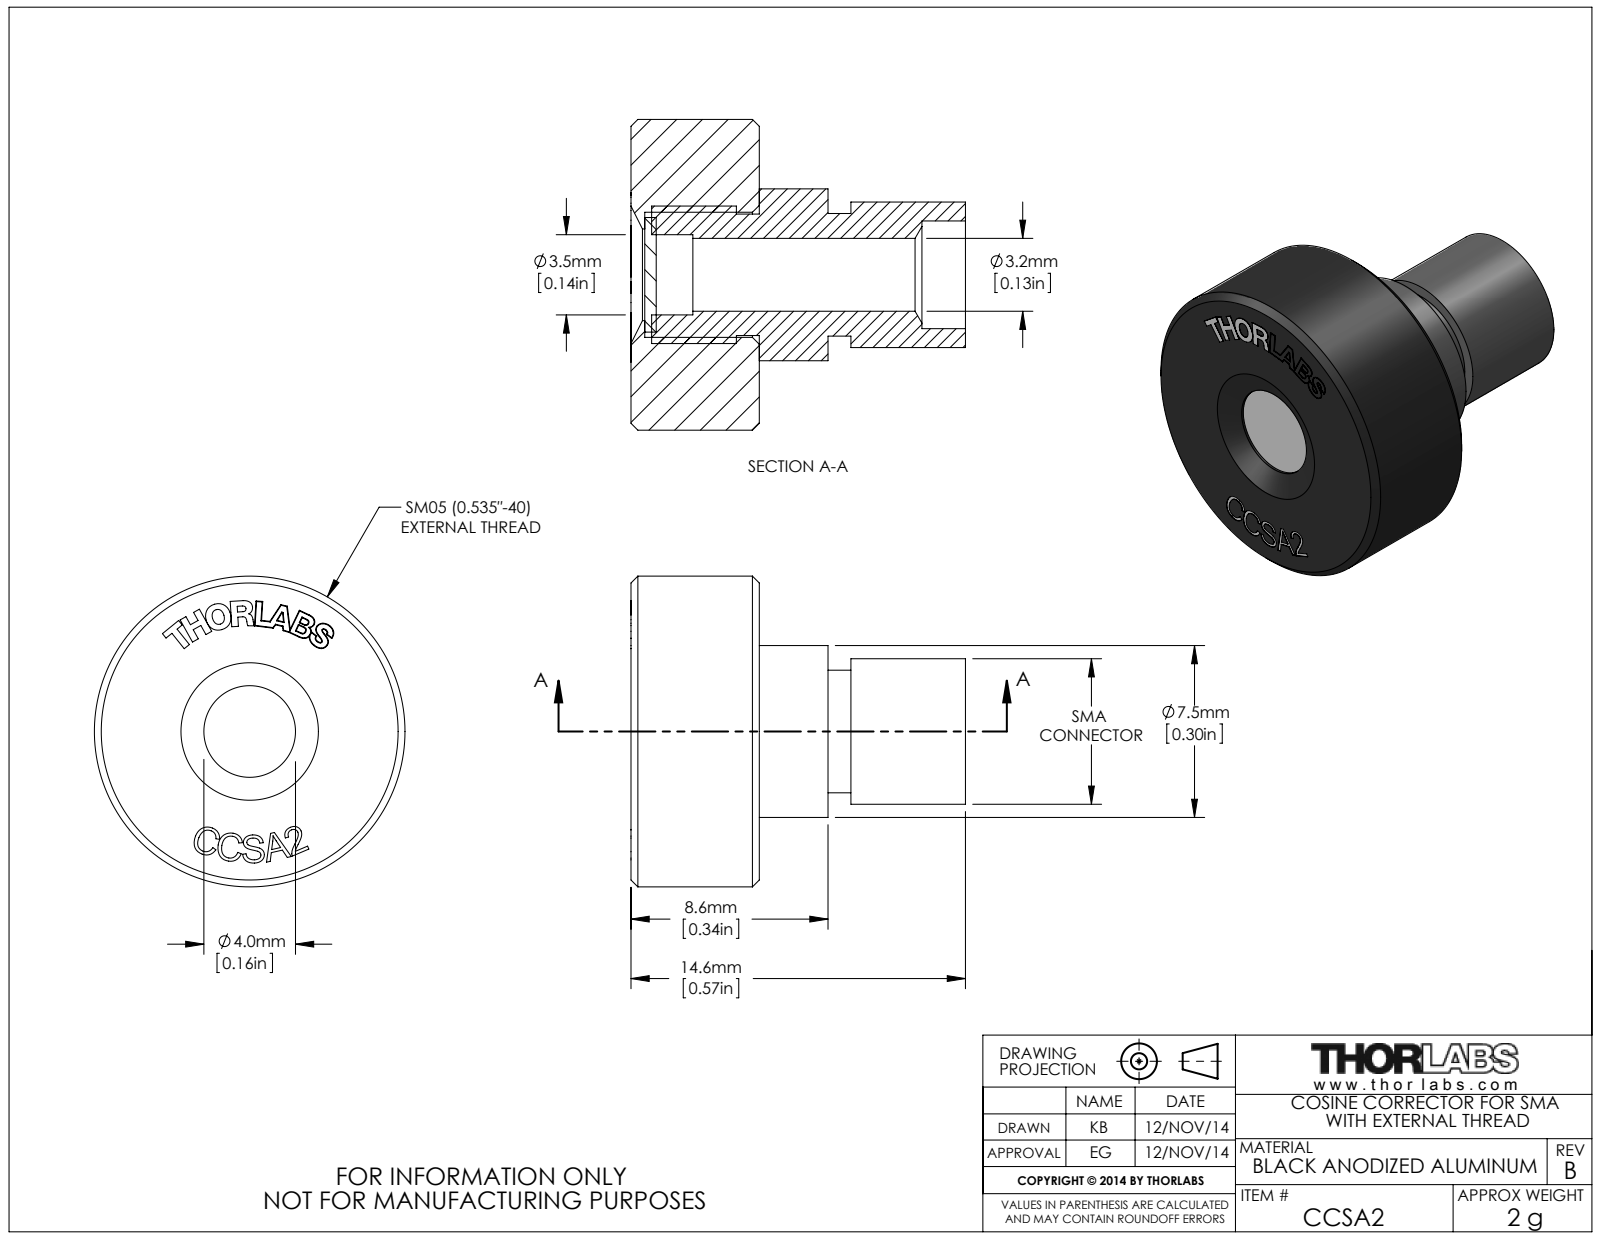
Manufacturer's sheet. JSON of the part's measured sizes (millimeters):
{"part_name": "CCSA2-inkl Spektralon-12.11.2014", "step_written_by": "SolidWorks 2014 (AUTOMOTIVE_DESIGN)", "units": "millimeters", "bodies": {"solids": 3, "faces": 341, "planar": 198, "cylindrical": 12, "other": 131}, "overall_size": [14.6, 13.56, 13.56], "volume_mm3": 995, "surface_area_mm2": 1143, "round_holes": [[3.18, 1], [3.5, 1], [4, 1], [4.7, 1], [5.46, 1]], "round_bosses_or_shafts": [[13.56, 1], [7.5, 1], [6.35, 1], [6, 1], [5.35, 1], [5.3, 1], [5, 1]], "face_to_face_distances": [5.6, 5, 0.6, 9, 8.6, 8, 3, 4, 1.1, 0.5]}
